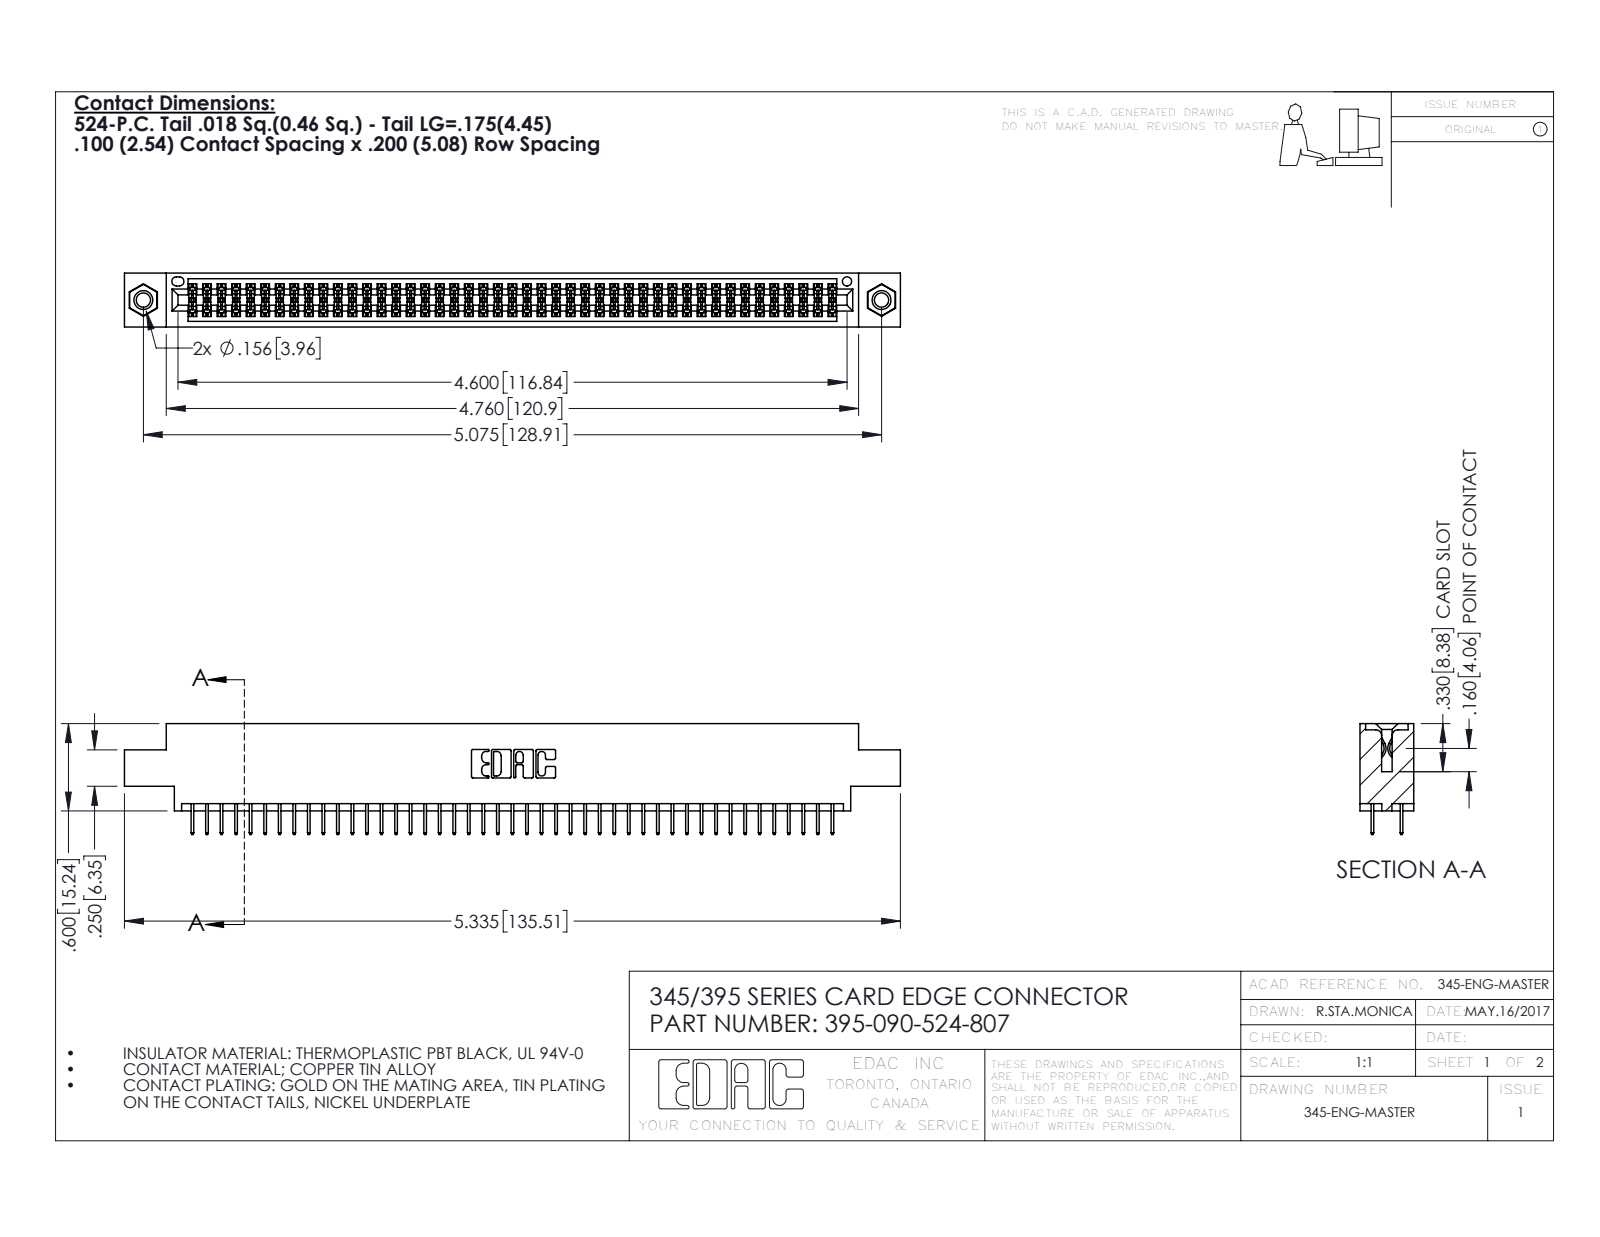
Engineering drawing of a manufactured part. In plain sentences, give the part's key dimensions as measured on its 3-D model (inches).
The part is named "395-090-524-807; 345-250-001_345-250-005-103; 345 Part_0.170 Offset - 0.156 Dia-TI; 345-292-001_345-293-124". Its 3-D file was written by "SolidWorks 2016 (CONFIG_CONTROL_DESIGN)". It is 93 solids with 5050 faces: 3626 planar, 1408 cylindrical and 16 other. Overall it measures 5.335 by 0.762 by 0.37 inches. Its volume is 0.789 cubic inches and its surface area 29.42 square inches. Round holes: 2 of diameter 0.098, 2 of diameter 0.125, 2 of diameter 0.156, 1 of diameter 0.064. Round bosses or shafts: 2 of diameter 0.155. Partial cylindrical surfaces (rounded edges, fillets, slot ends): 135 of radius 0.006, 22 of radius 0.01, 6 of radius 0.007, 6 of radius 0.031, 3 of radius 0.026, 2 of radius 0.014, 2 of radius 0.019, 2 of radius 0.022. The main face-to-face distances are 0.072, 0.298, 0.37, 0.2, 0.098, 0.272, 0.025, 0.225, 0.175, 0.072. The hole center spacings are 0.27, 4.839, 5.075.
